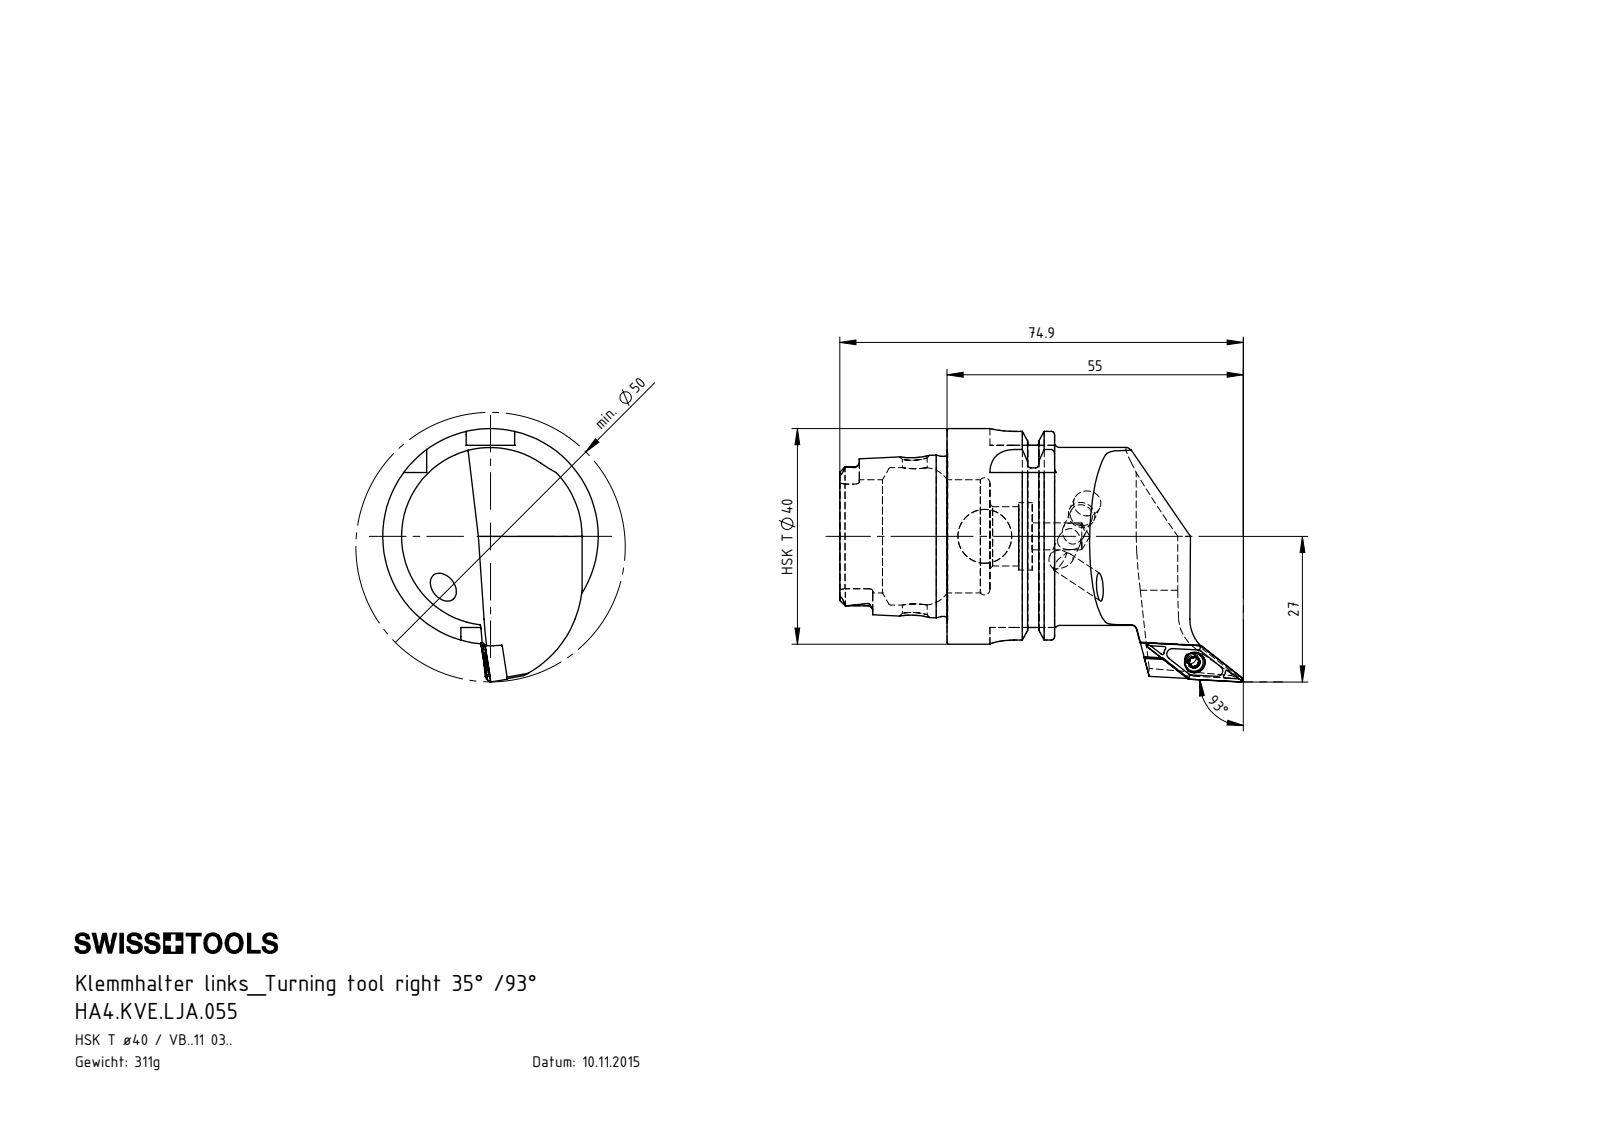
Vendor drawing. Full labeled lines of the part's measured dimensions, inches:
Part name (STEP PRODUCT): HA4-KVE.LJA.055_A; WCA-ER2.001.006_A; KVT_MB_600_050; HA4.KVE.LJA.055 (+1 more)
STEP written by: SolidWorks 2017 (AUTOMOTIVE_DESIGN)
Units: inches
Bodies: 5 solids, 236 faces (83 planar, 60 cylindrical, 93 other)
Overall size (bounding box): 2.949 × 1.85 × 1.575
Volume: 2.412 in³ · Surface area: 20.5 in²
Round holes (diameter × count): ⌀0.165 ×2, ⌀0.197 ×2, ⌀0.081 ×1, ⌀0.11 ×1, ⌀0.152 ×1, ⌀0.157 ×1, ⌀0.181 ×1, ⌀0.394 ×1, ⌀0.433 ×1, ⌀0.492 ×1, ⌀0.827 ×1, ⌀1.004 ×1
Round bosses / shafts (diameter × count): ⌀1.575 ×1, ⌀1.368 ×1, ⌀1.299 ×1, ⌀1.17 ×1, ⌀0.197 ×1, ⌀0.134 ×1, ⌀0.098 ×1
Partial cylindrical surfaces — rounded edges, fillets, slot ends (radius × count): R0.008 ×6, R0.035 ×6, R0.014 ×5, R0.074 ×4, R0.177 ×4, R0.014 ×1, R0.118 ×1, R0.276 ×1
Main face-to-face distances: 0.313, 0.785, 0.472, 0.783, 1.096, 1.569, 0.113, 1.406, 0.622, 0.309
